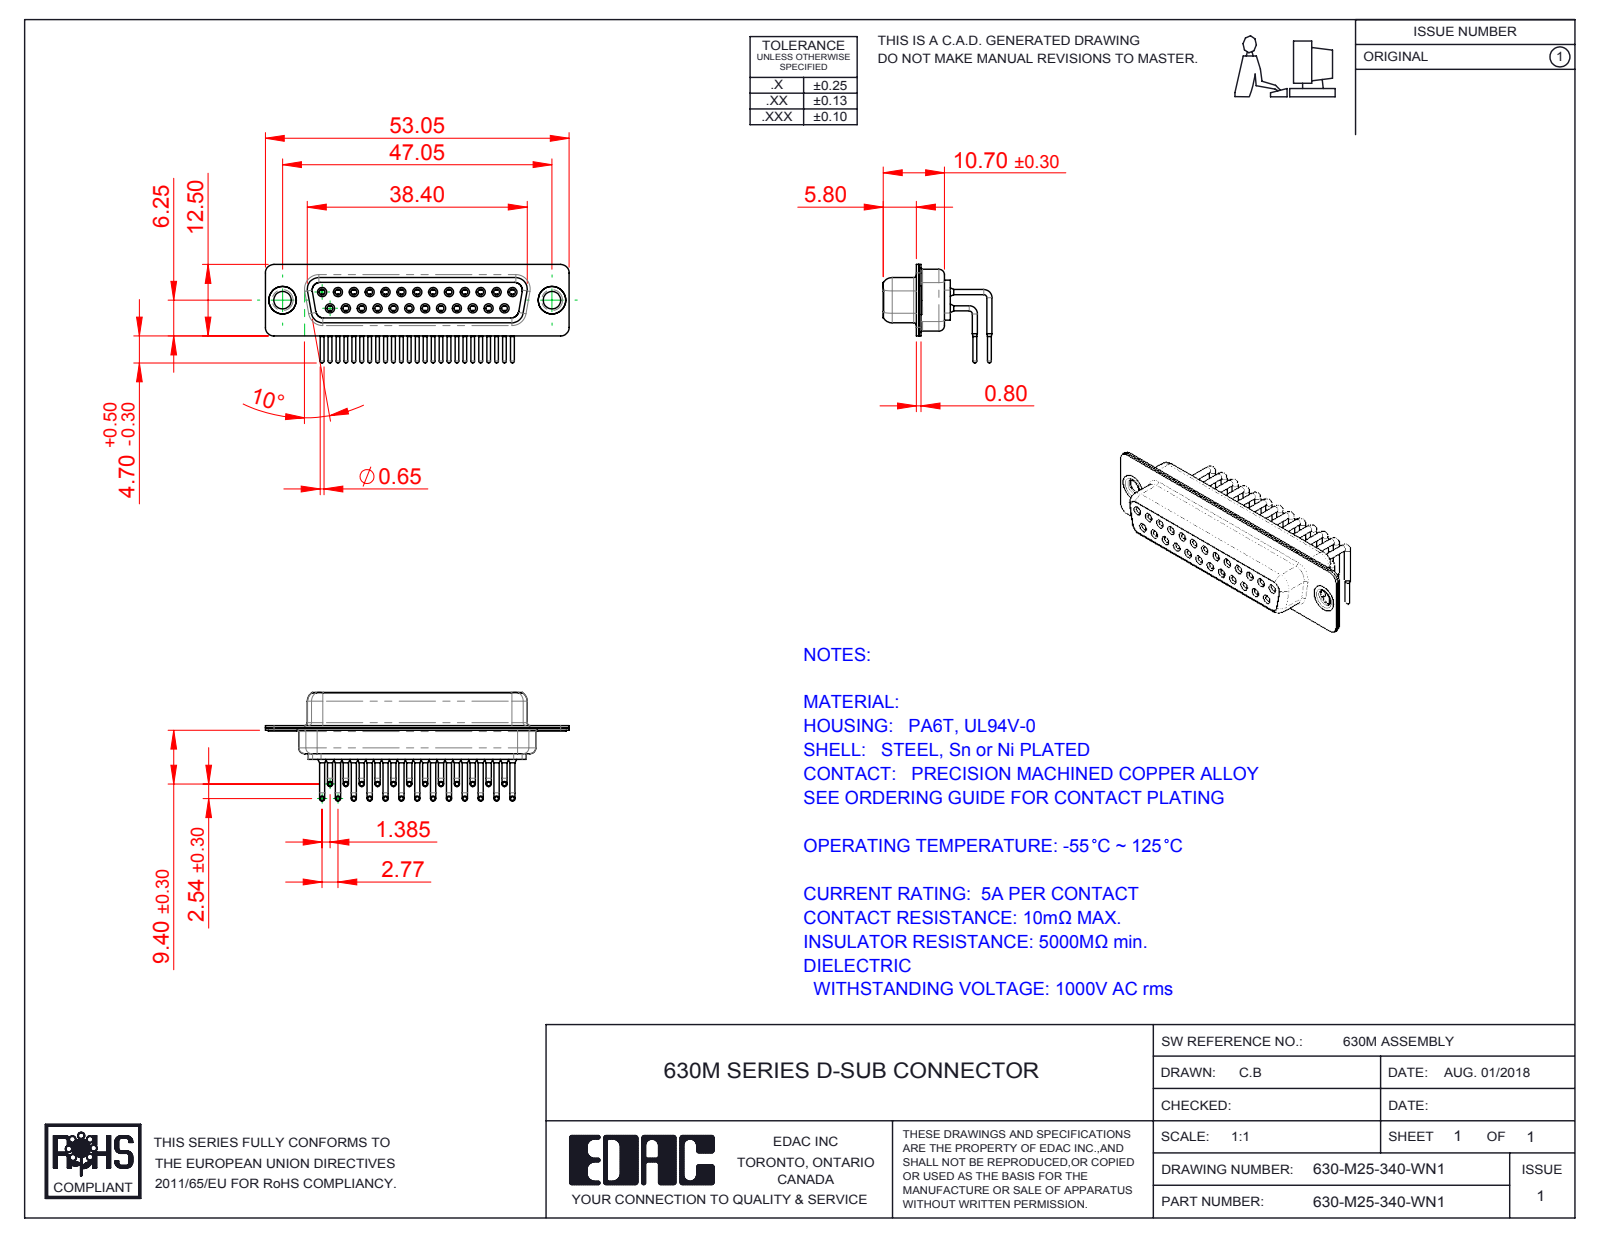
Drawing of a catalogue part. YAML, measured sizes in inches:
part_name: "630M Housing_25 Contacts; 630M Shell Front_25 Contacts; 630M Contact Row 1; 630M Thru Hole Rivet (+3 more)"
step_written_by: "SolidWorks 2016 (CONFIG_CONTROL_DESIGN)"
units: inches
bodies: {solids: 30, faces: 1578, planar: 442, cylindrical: 696, other: 440}
overall_size: [2.089, 0.748, 0.677]
volume: 0.233
surface_area: 14.85
round_holes:
  - {diameter: 0.039, count: 25}
  - {diameter: 0.043, count: 25}
  - {diameter: 0.067, count: 25}
  - {diameter: 0.071, count: 25}
  - {diameter: 0.079, count: 25}
  - {diameter: 0.12, count: 2}
  - {diameter: 0.157, count: 2}
  - {diameter: 0.189, count: 2}
round_bosses_or_shafts:
  - {diameter: 0.035, count: 50}
  - {diameter: 0.063, count: 25}
  - {diameter: 0.059, count: 25}
  - {diameter: 0.026, count: 25}
  - {diameter: 0.197, count: 2}
  - {diameter: 0.193, count: 2}
  - {diameter: 0.14, count: 2}
partial_cylinders:
  - {radius: 0.059, count: 16}
  - {radius: 0.079, count: 12}
  - {radius: 0.053, count: 10}
  - {radius: 0.063, count: 8}
  - {radius: 0.01, count: 4}
  - {radius: 0.02, count: 4}
  - {radius: 0.024, count: 4}
  - {radius: 0.026, count: 4}
face_to_face_distances: [0.016, 0.057, 0.352, 0.244, 0.075, 0.335, 0.278, 0.018, 0.091, 0.033]
hole_center_spacings: [0.124, 0.109, 0.218, 0.327, 0.436, 0.545, 0.198, 0.295]
